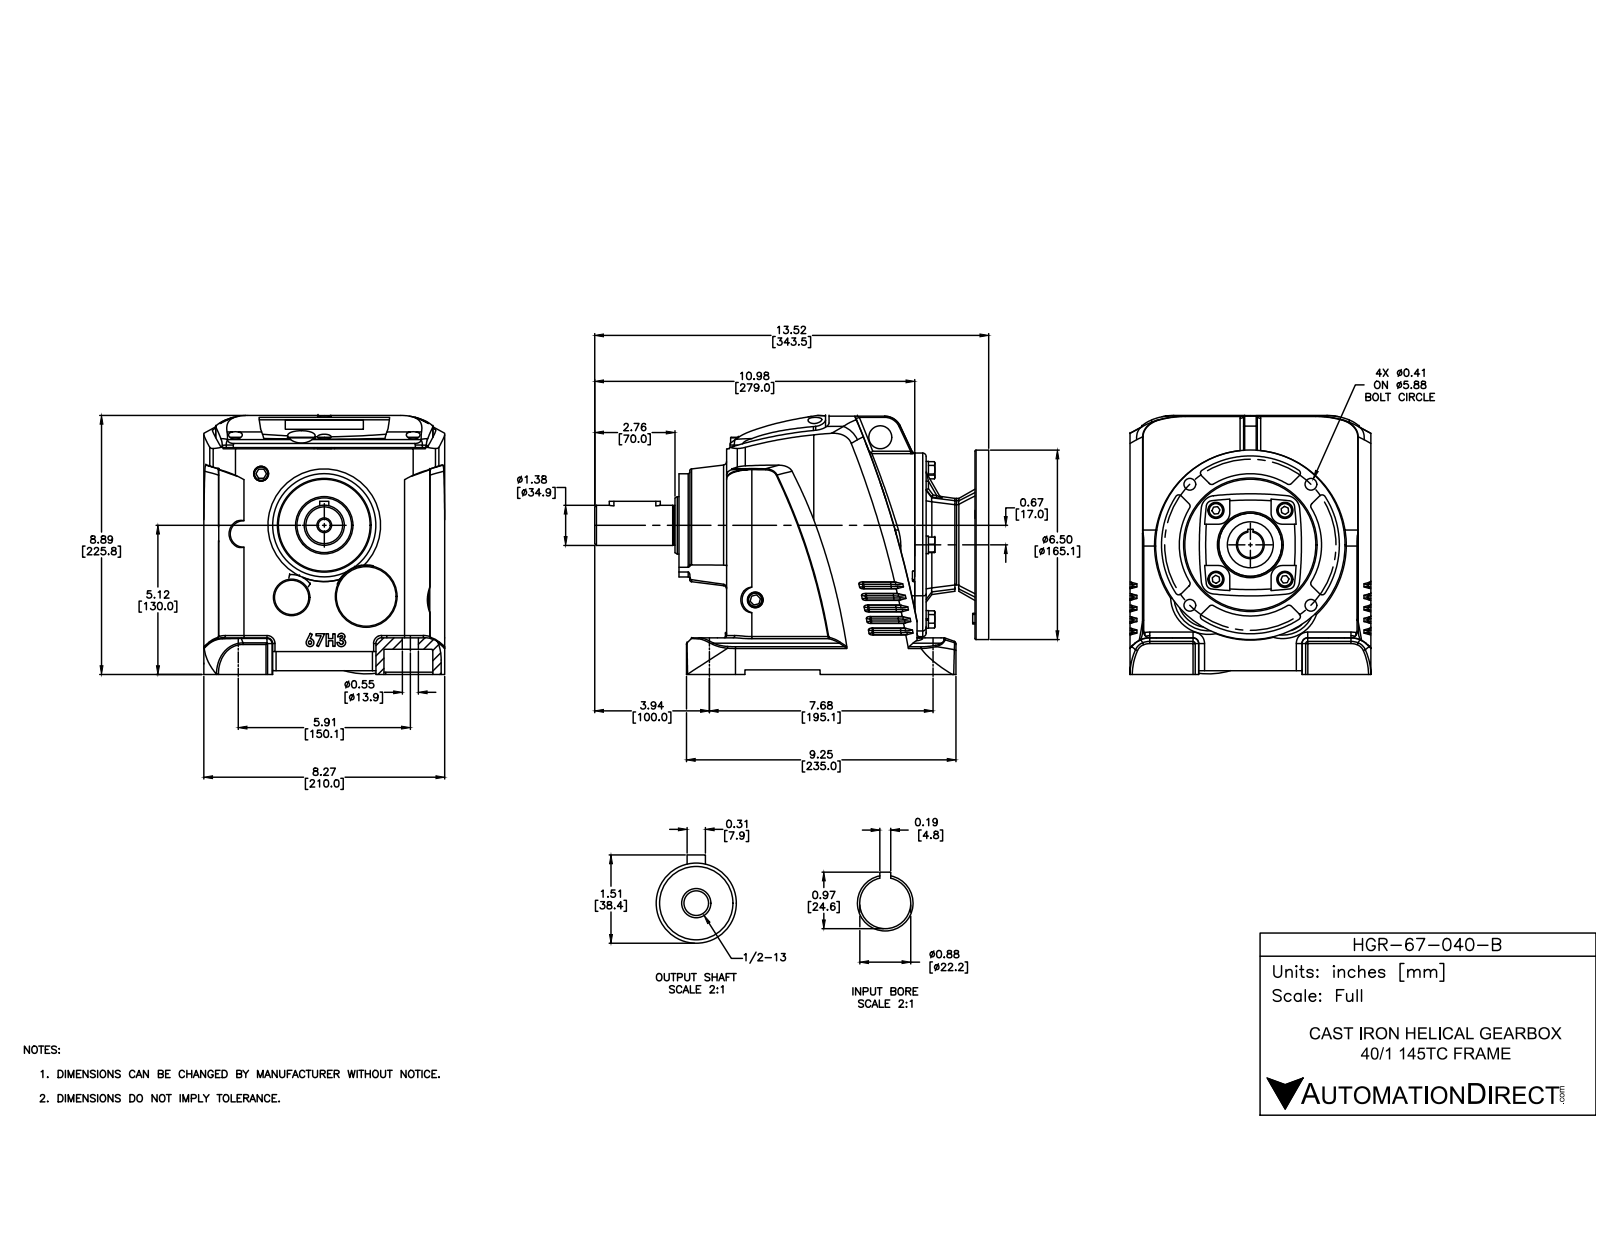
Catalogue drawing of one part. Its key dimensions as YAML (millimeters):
part_name: "HGR-67-005-B"
step_written_by: "SolidWorks 2015 (CONFIG_CONTROL_DESIGN)"
units: millimeters
bodies: {solids: 30, faces: 1083, planar: 364, cylindrical: 278, other: 441}
overall_size: [343.5, 225.8, 210]
volume: 6855000
surface_area: 523400
round_holes:
  - {diameter: 14, count: 8}
  - {diameter: 12, count: 6}
  - {diameter: 10.3, count: 4}
  - {diameter: 10.7, count: 1}
  - {diameter: 20, count: 1}
  - {diameter: 22.2, count: 1}
  - {diameter: 40, count: 1}
  - {diameter: 50, count: 1}
  - {diameter: 114.3, count: 1}
round_bosses_or_shafts:
  - {diameter: 15.4, count: 4}
  - {diameter: 13, count: 4}
  - {diameter: 12.6, count: 4}
  - {diameter: 10, count: 3}
  - {diameter: 165.1, count: 1}
  - {diameter: 160, count: 1}
  - {diameter: 90, count: 1}
  - {diameter: 80, count: 1}
partial_cylinders:
  - {radius: 2, count: 45}
  - {radius: 3, count: 21}
  - {radius: 5, count: 7}
  - {radius: 1, count: 4}
  - {radius: 10, count: 4}
  - {radius: 13, count: 3}
  - {radius: 20, count: 3}
  - {radius: 0.2, count: 2}
face_to_face_distances: [1, 7, 13, 197, 216.5, 164, 10, 12, 52.5, 210]
hole_center_spacings: [85.9, 32.1, 42.5, 60.1, 74.6, 105.5, 117.1, 29.1]
